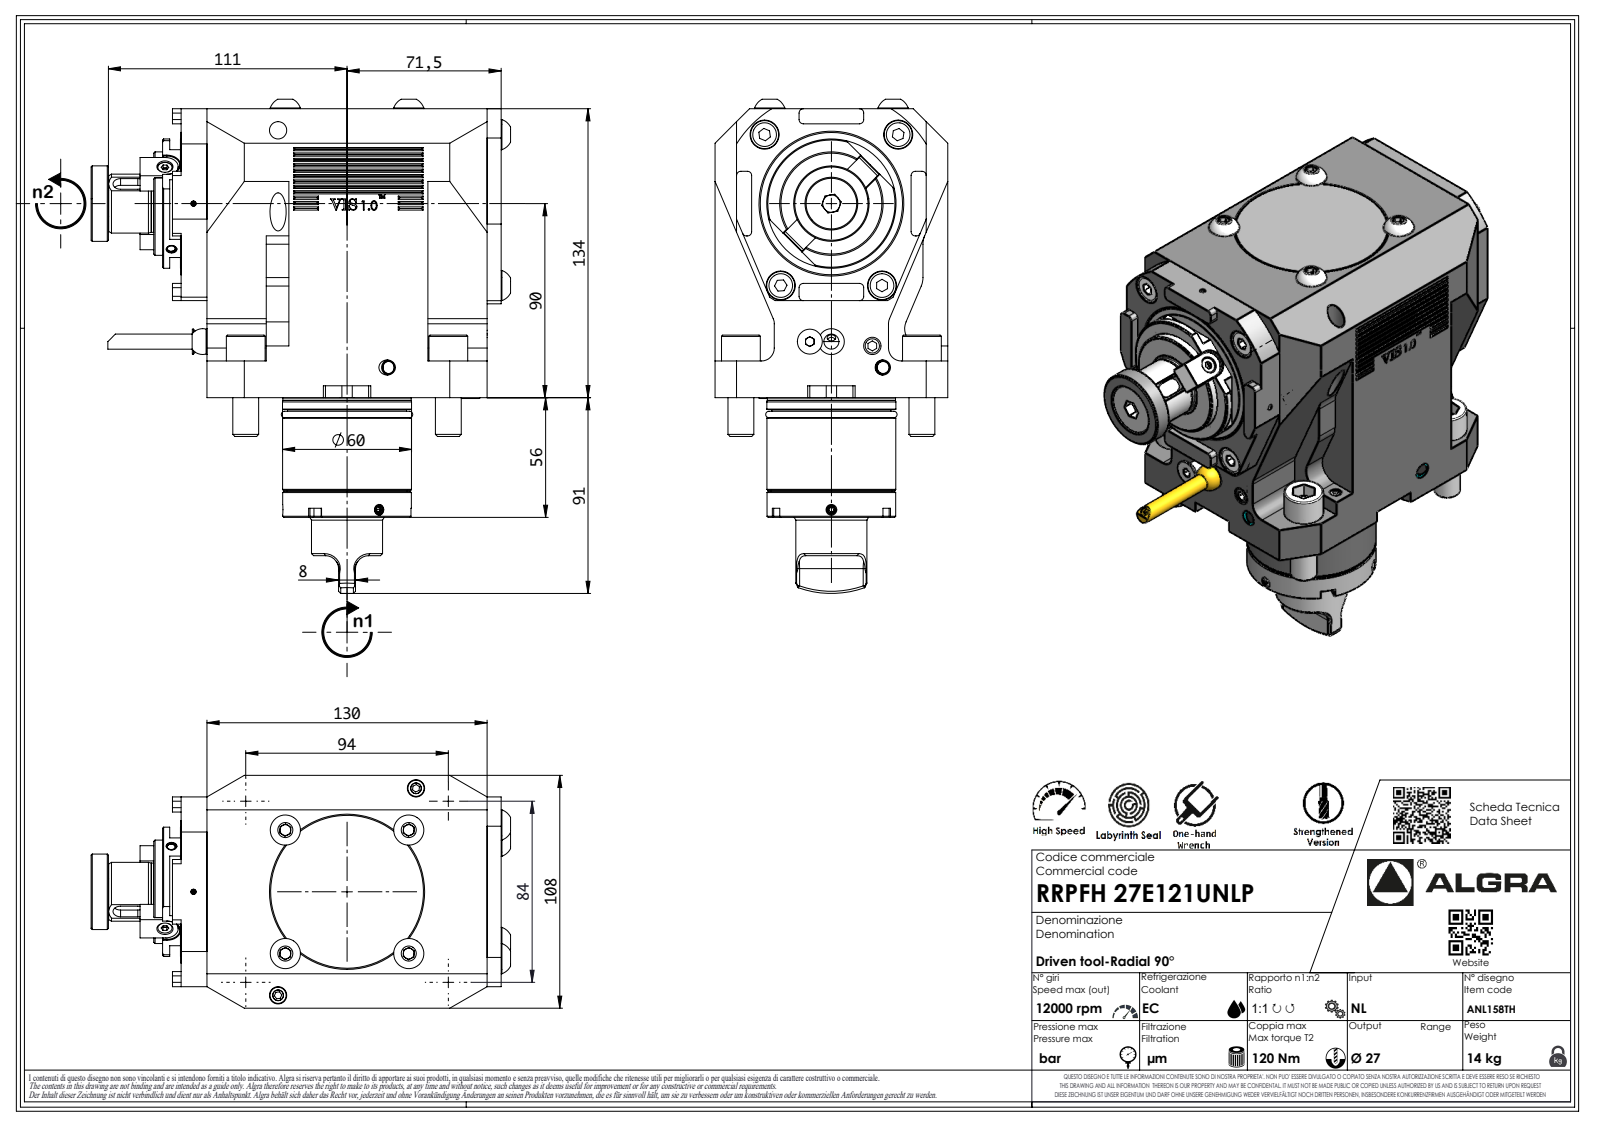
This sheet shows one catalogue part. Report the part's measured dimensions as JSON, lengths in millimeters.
{"part_name": "RRPFH27E121UNLP", "step_written_by": "SolidWorks 2023 (AUTOMOTIVE_DESIGN)", "units": "millimeters", "bodies": {"solids": 1, "faces": 1016, "planar": 704, "cylindrical": 138, "other": 174}, "overall_size": [224.8, 190.1, 108], "volume_mm3": 2029000, "surface_area_mm2": 130591, "round_holes": [[2.1, 1], [4, 1]], "round_bosses_or_shafts": [[18, 4], [12, 4], [60, 1], [59.9, 1], [59.8, 1], [59.7, 1], [59.5, 1], [55.2, 1]], "partial_cylinders_radius": [[0.2, 21], [8, 18], [2, 16], [6, 14], [0.33, 7], [0.52, 7], [3.7, 7], [10, 4]], "face_to_face_distances": [108, 134, 27.5, 12, 102.5, 6.5, 136.5, 5.5, 148.5, 39.5]}
